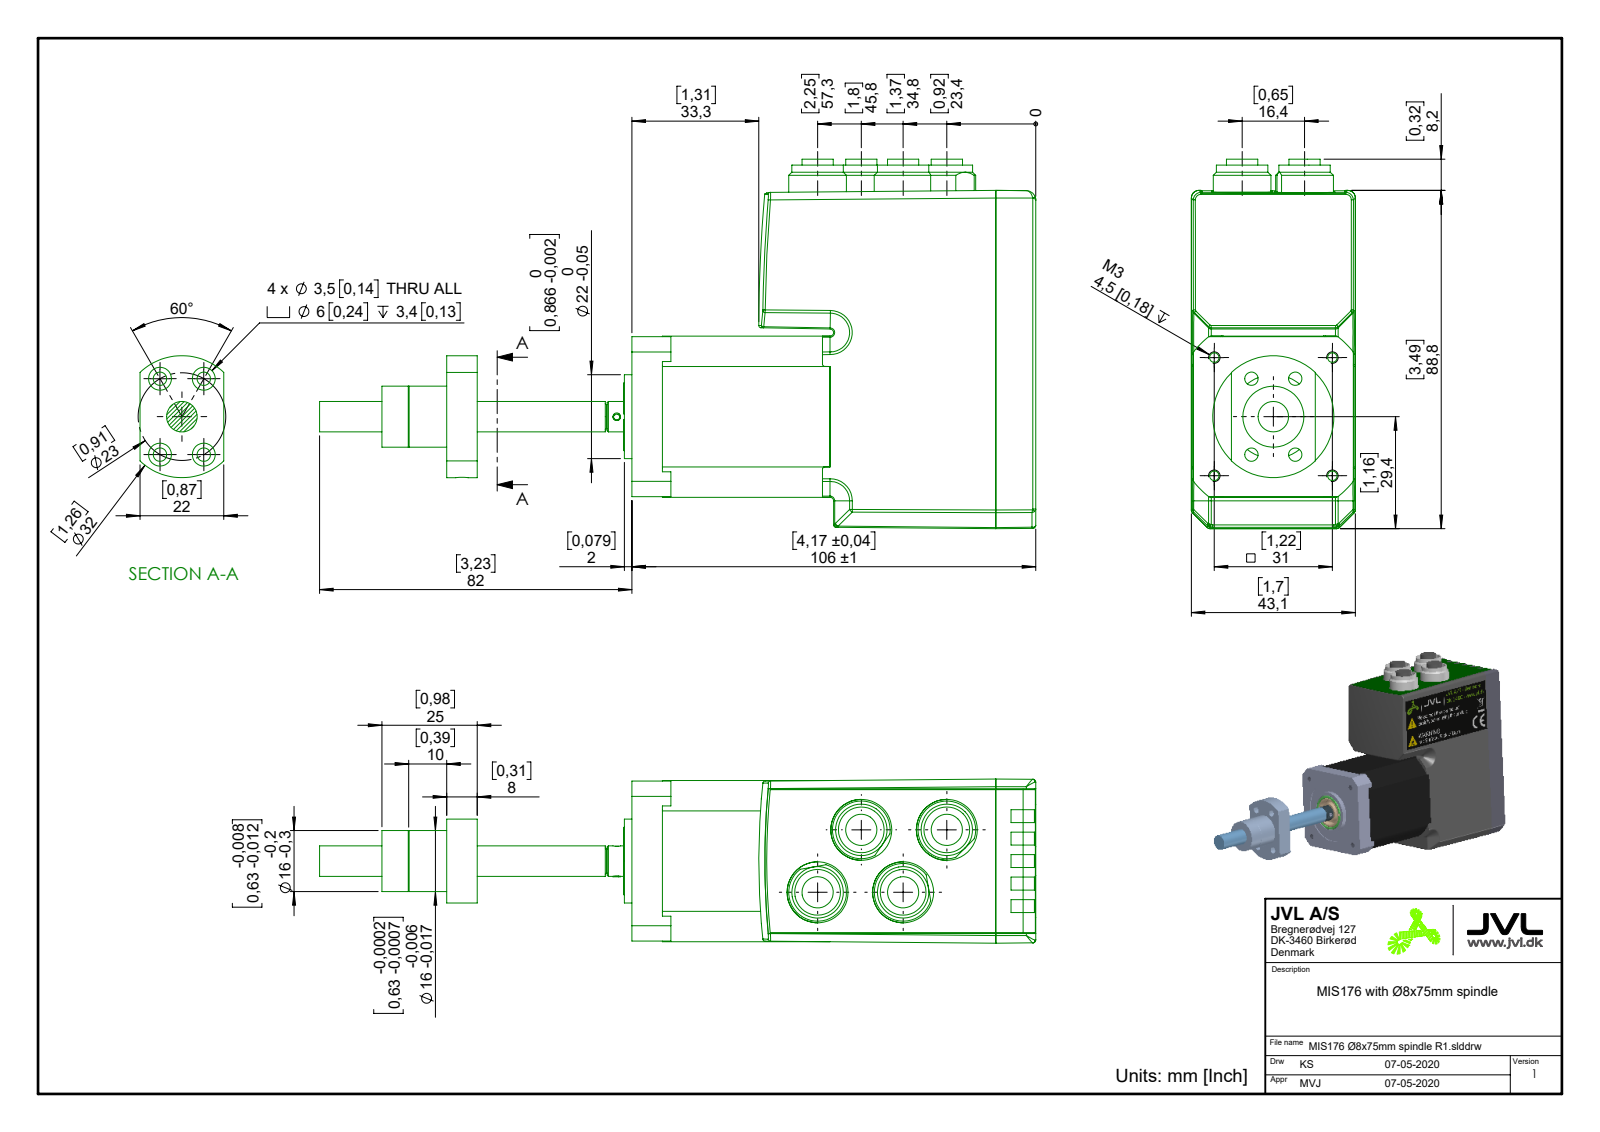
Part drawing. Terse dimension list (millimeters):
name: MIS176 Ø8x75mm spindle R1
written by: SolidWorks 2018 (AUTOMOTIVE_DESIGN)
unit: mm
bodies: 5 solids, 508 faces (189 planar, 200 cylindrical, 119 other)
size: 188 × 96.94 × 43.06
volume: 330 256 mm³; area: 43 737 mm²
holes: 4× ⌀2.5, 4× ⌀3.5, 4× ⌀6, 4× ⌀12, 4× ⌀16, 3× ⌀3.3, 1× ⌀2, 1× ⌀6.35, 1× ⌀8.3, 1× ⌀9, 1× ⌀10, 1× ⌀31.8
bosses: 4× ⌀15.15, 4× ⌀13.5, 4× ⌀8.2, 1× ⌀22, 1× ⌀16, 1× ⌀15.5, 1× ⌀13.9, 1× ⌀8
rounds: 30× R1, 3× R0.8, 2× R0.93, 2× R2, 2× R3.8, 2× R4.2, 1× R0.35, 1× R0.6
face distances: 42.3, 43.07, 42.15, 105.9, 42, 106, 8, 2, 40.63, 146.53
hole spacings: 11.5, 11.21, 20, 21.92, 21.96, 22.45, 27.26, 31
